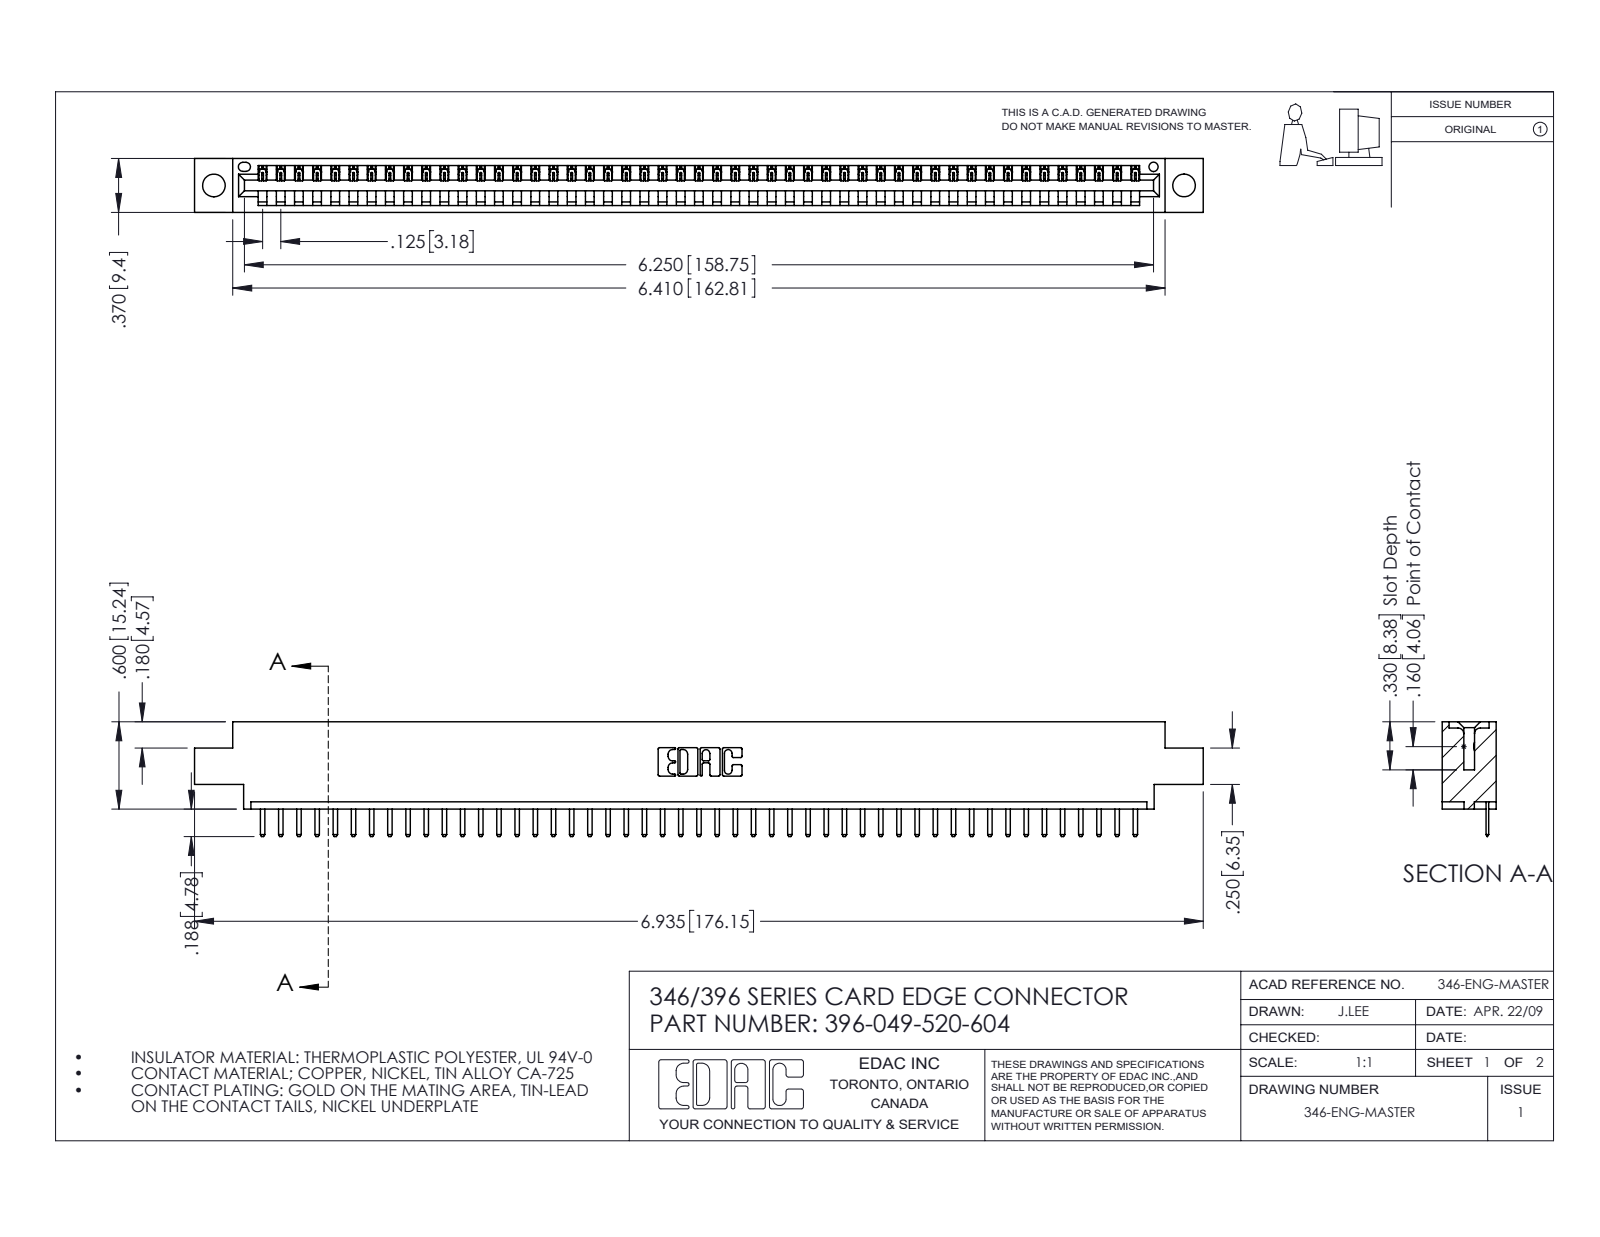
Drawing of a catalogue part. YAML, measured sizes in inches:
part_name: "345-292-001_345-293-120; 346 Part_0.170 Offset - 0.156 Dia-TH; 396-049-520-604"
step_written_by: "SolidWorks 2016 (CONFIG_CONTROL_DESIGN)"
units: inches
bodies: {solids: 50, faces: 3164, planar: 2138, cylindrical: 1026, other: 0}
overall_size: [6.935, 0.788, 0.37]
volume: 1.008
surface_area: 31.35
round_holes:
  - {diameter: 0.156, count: 2}
  - {diameter: 0.064, count: 1}
partial_cylinders:
  - {radius: 0.01, count: 100}
  - {radius: 0.006, count: 98}
  - {radius: 0.01, count: 22}
  - {radius: 0.007, count: 6}
  - {radius: 0.031, count: 6}
  - {radius: 0.026, count: 3}
  - {radius: 0.031, count: 2}
  - {radius: 0.04, count: 2}
face_to_face_distances: [0.048, 0.322, 0.37, 0.25, 0.148, 0.222, 0.1, 0.174, 0.072, 0.298]
hole_center_spacings: [0.246, 6.461, 6.67]
